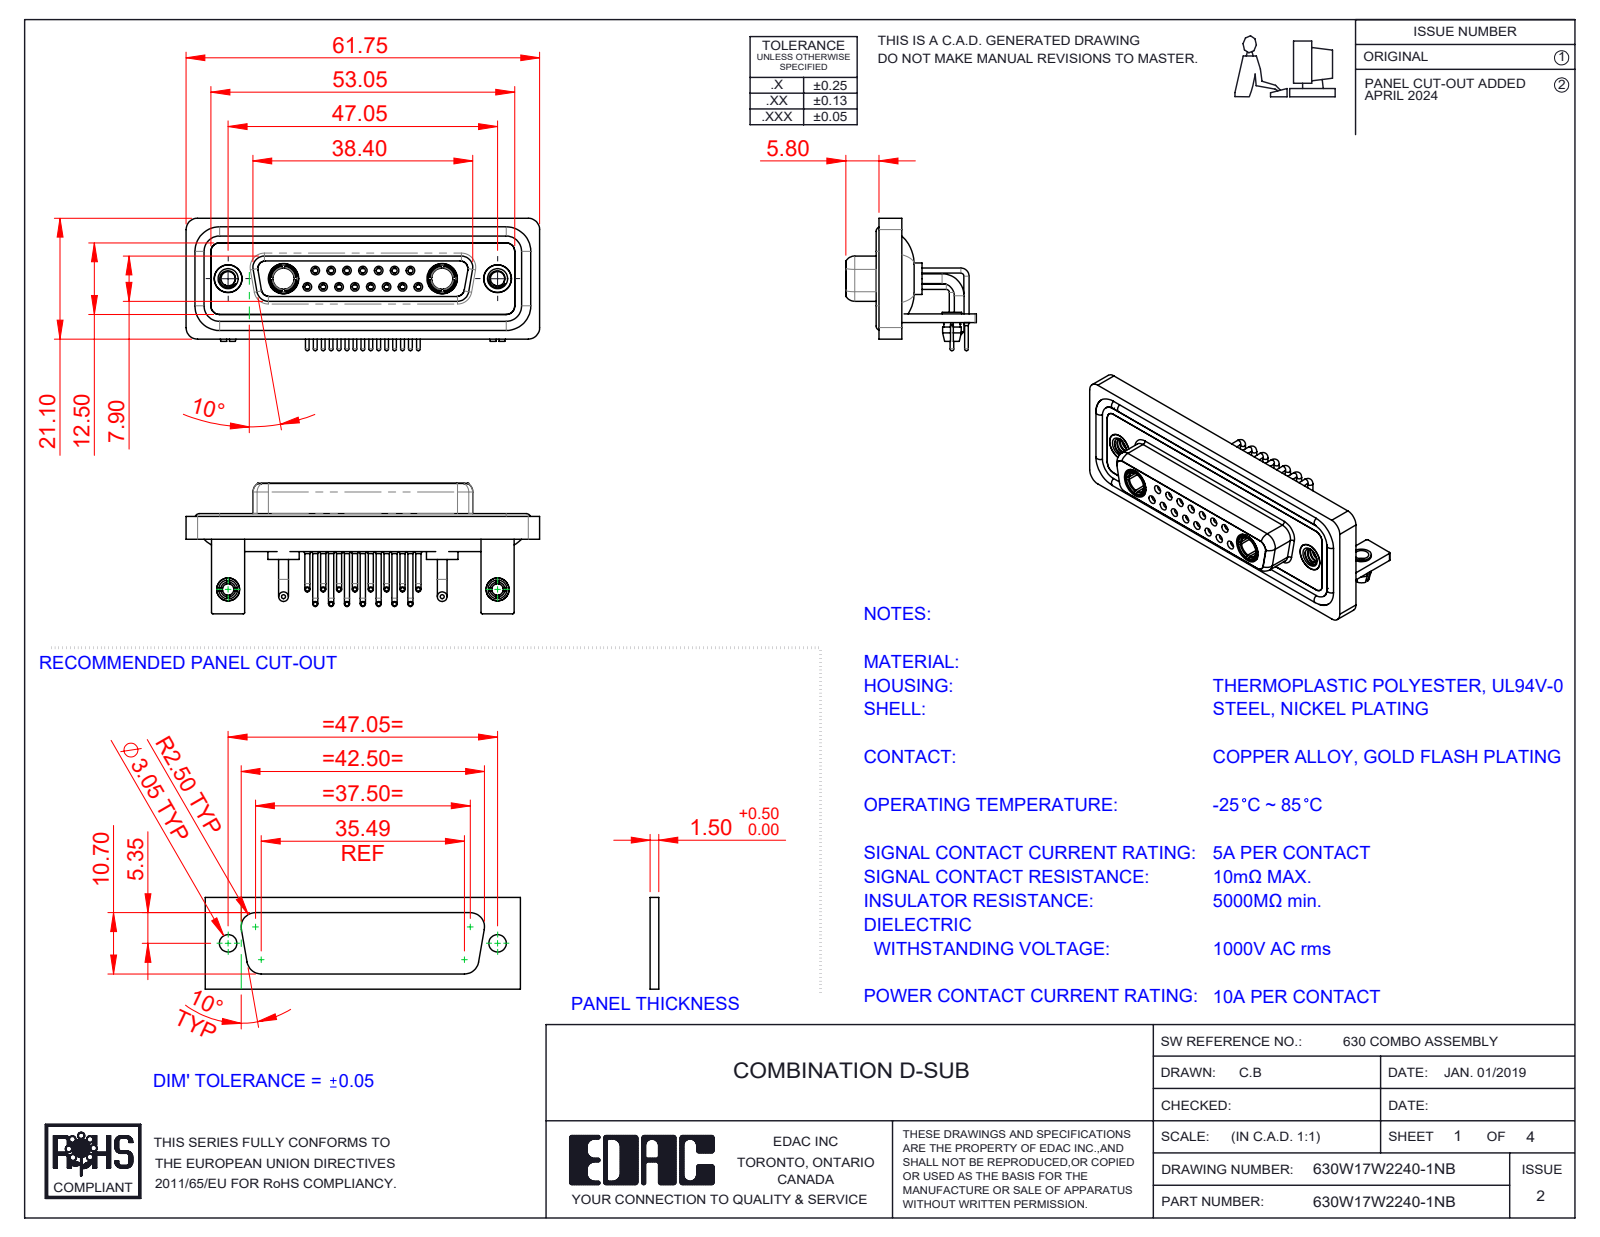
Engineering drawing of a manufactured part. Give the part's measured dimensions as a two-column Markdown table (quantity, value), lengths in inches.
| quantity | value |
| --- | --- |
| part name | 630Combo Housing_17W2; 630Combo Stabilizer Bracket_50 Contacts; 630Combo Board Lock_50 Contacts; 630W17W2240-1NB (+7 more) |
| STEP written by | SolidWorks 2023 (CONFIG_CONTROL_DESIGN) |
| units | inches |
| bodies | 30 solids, 1471 faces (456 planar, 637 cylindrical, 378 other) |
| overall size | 2.431 × 0.91 × 0.898 |
| volume | 0.535 in³ |
| surface area | 23.84 in² |
| round holes (diameter × count) | 0.079 × 17, 0.035 × 15, 0.043 × 15, 0.059 × 15, 0.063 × 8, 0.067 × 7, 0.098 × 4, 0.191 × 4, 0.126 × 2, 0.146 × 2, 0.157 × 2, 0.159 × 2 |
| round bosses / shafts (diameter × count) | 0.035 × 15, 0.026 × 15, 0.063 × 11, 0.067 × 4, 0.217 × 2, 0.205 × 2, 0.195 × 2, 0.195 × 2 |
| partial cylindrical surfaces (radius × count) | 0.079 × 19, 0.059 × 18, 0.01 × 16, 0.053 × 8, 0.063 × 8, 0.02 × 5, 0.024 × 4, 0.026 × 4 |
| main face-to-face distances | 0.016, 0.071, 0.114, 0.059, 0.146, 0.161, 0.043, 0.055, 0.063, 0.122 |
| hole center spacings | 0.124, 0.109, 0.218, 0.327, 0.198, 0.295, 0.436, 0.198 |
